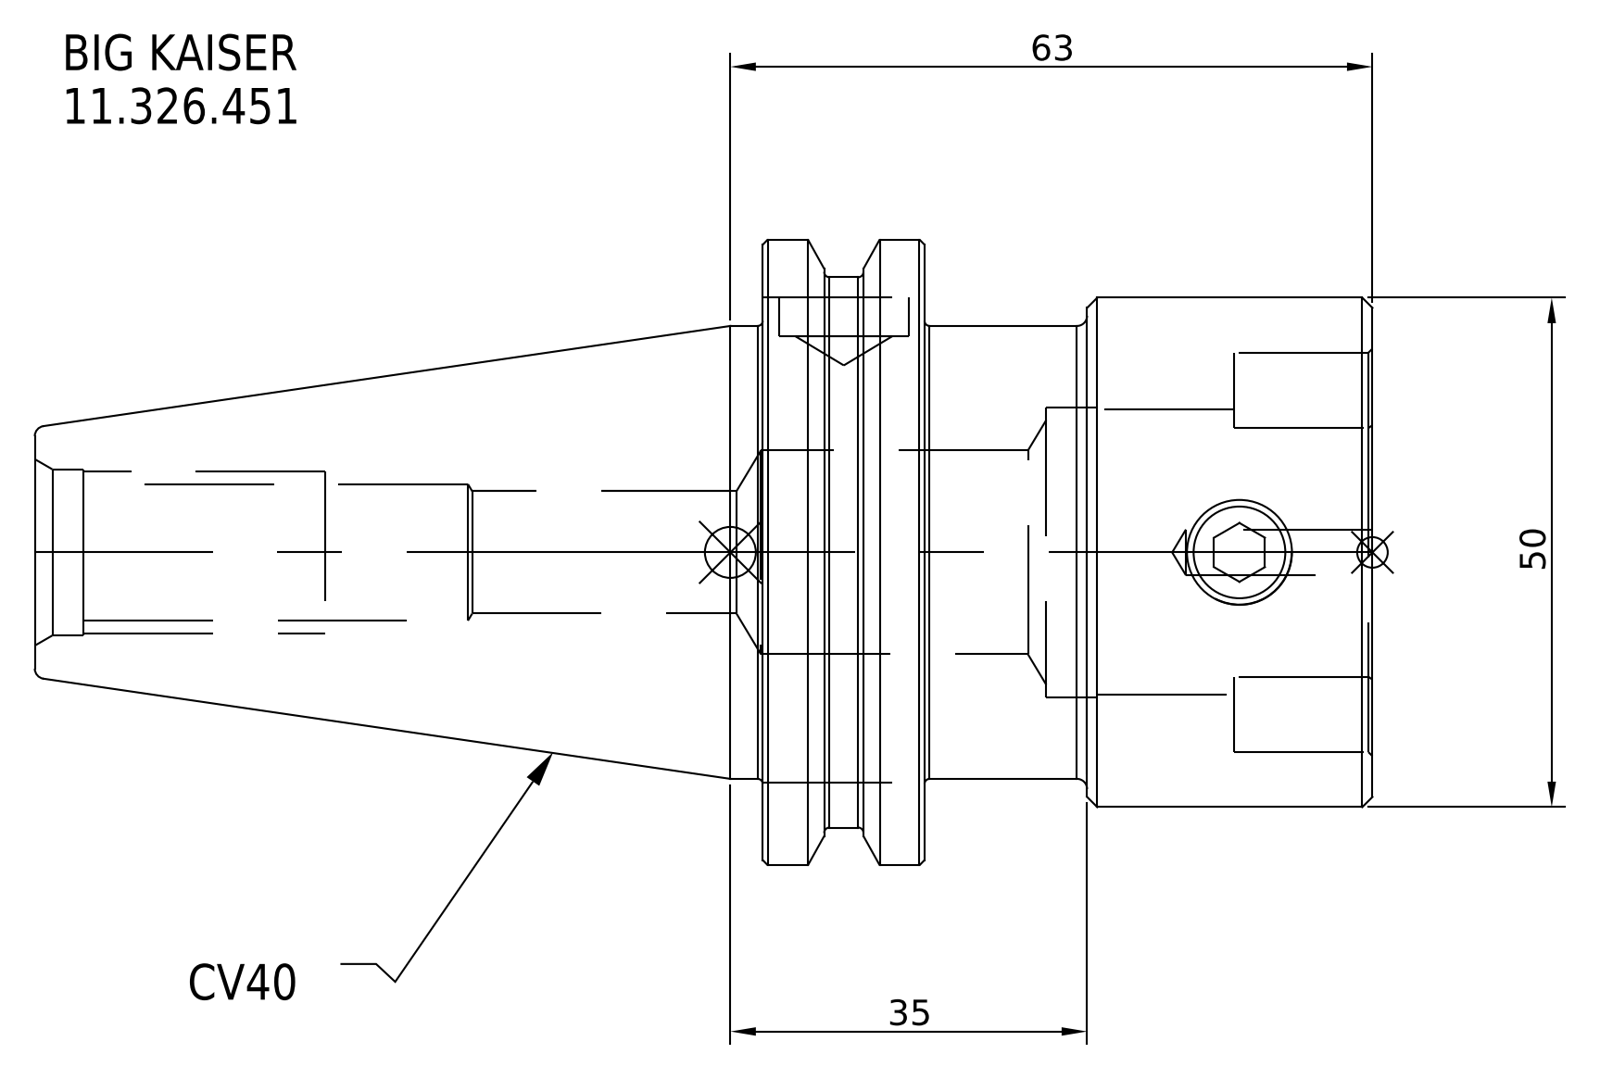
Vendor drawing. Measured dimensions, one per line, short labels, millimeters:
name: 11_326_451
written by: SolidWorks 2021 (CONFIG_CONTROL_DESIGN)
unit: mm
bodies: 2 solids, 17 faces (8 planar, 6 cylindrical, 3 other)
size: 131.25 × 63.5 × 63.5
volume: 197 024 mm³; area: 27 675 mm²
bosses: 1× ⌀63.5, 1× ⌀56.36, 1× ⌀50, 1× ⌀44.45
face distances: 27.95, 59.83, 31.88, 43.95, 16, 15.88, 131.25, 103.3, 87.3, 71.42
